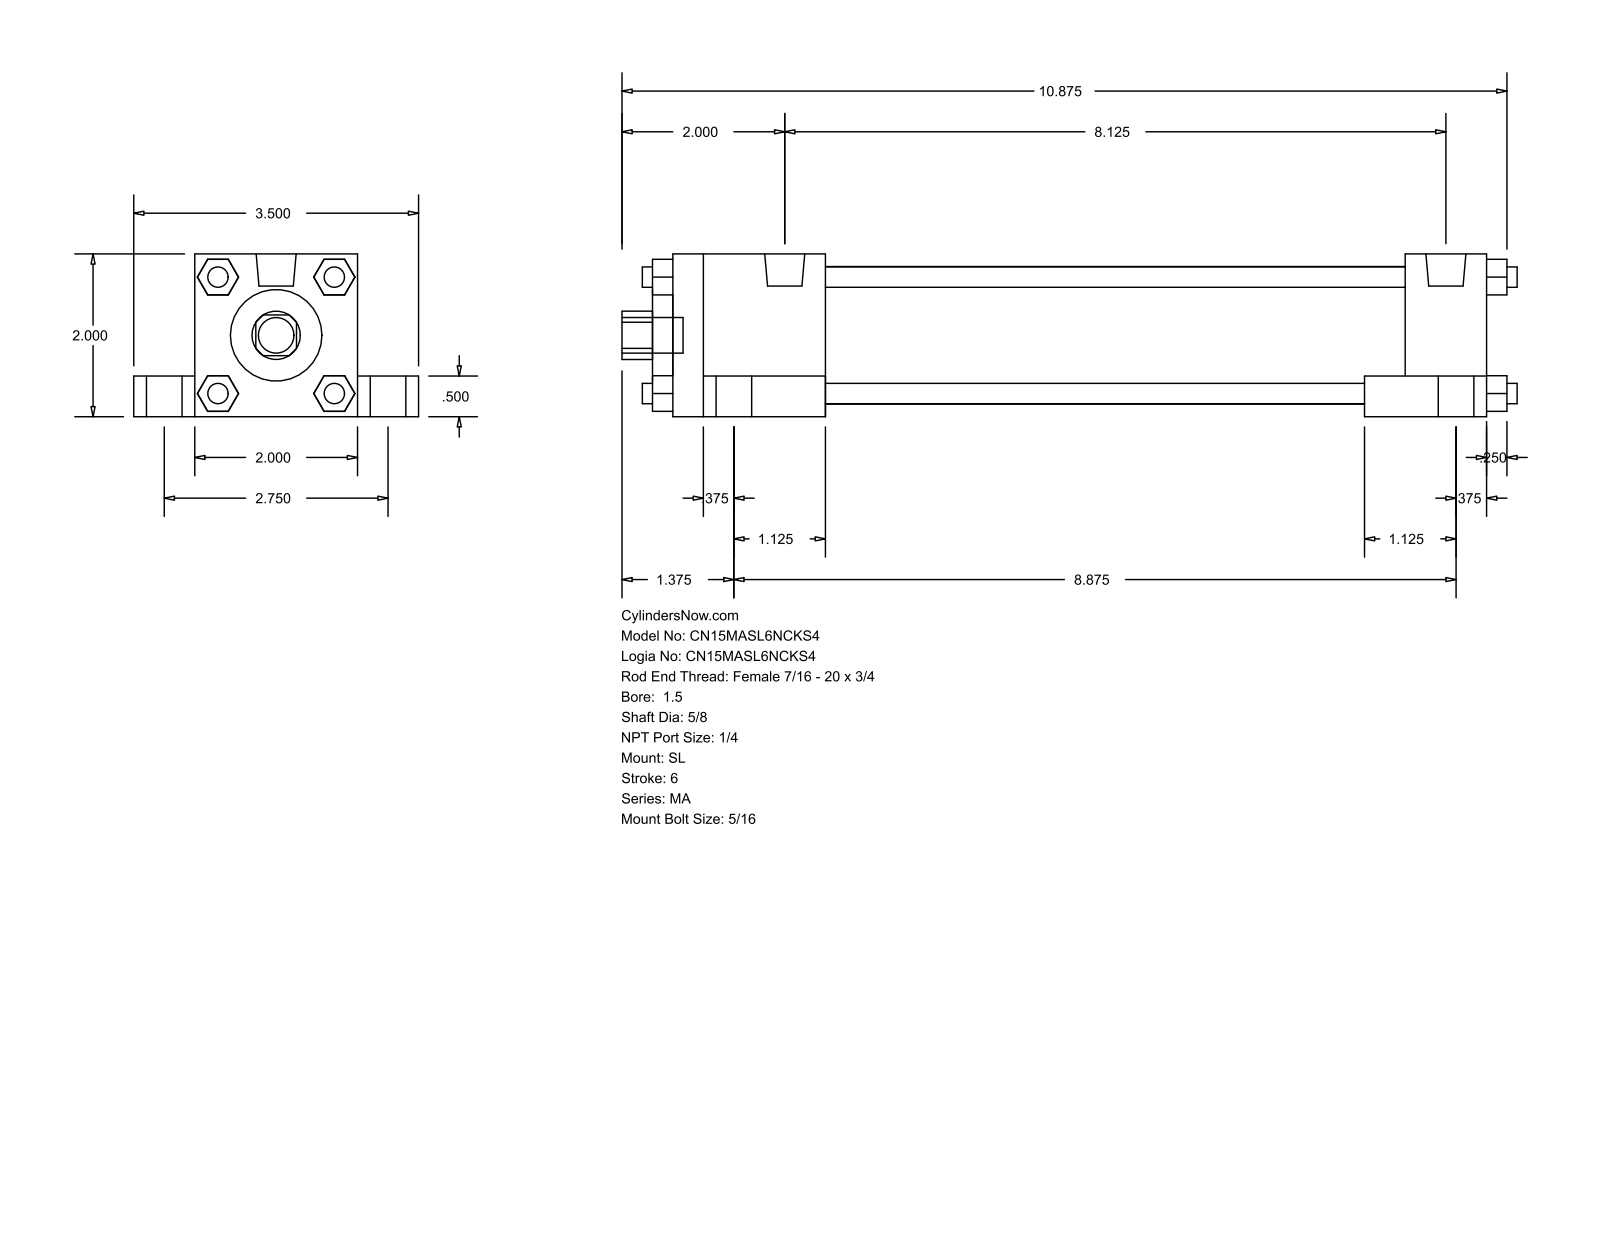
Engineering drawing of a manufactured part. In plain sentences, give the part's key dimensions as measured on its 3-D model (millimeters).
The part is named "MA_SL__0150_0.625". Its 3-D file was written by "GSSL Pune (CONFIG_CONTROL_DESIGN)". It is 0 solids with 148 faces: 112 planar, 36 cylindrical and 0 other. Overall it measures 279.4 by 88.9 by 50.8 millimeters. Round holes: 1 of diameter 15.88, 1 of diameter 28.57, 1 of diameter 42.93. Round bosses or shafts: 5 of diameter 11.11, 4 of diameter 17.46, 4 of diameter 7.94, 4 of diameter 6.35, 2 of diameter 12.49. Partial cylindrical surfaces (rounded edges, fillets, slot ends): 1 of radius 7.54. The main face-to-face distances are 50.8, 19.05, 38.1, 12.7, 254, 69.85, 180.97, 9.52, 6.35, 260.35.
